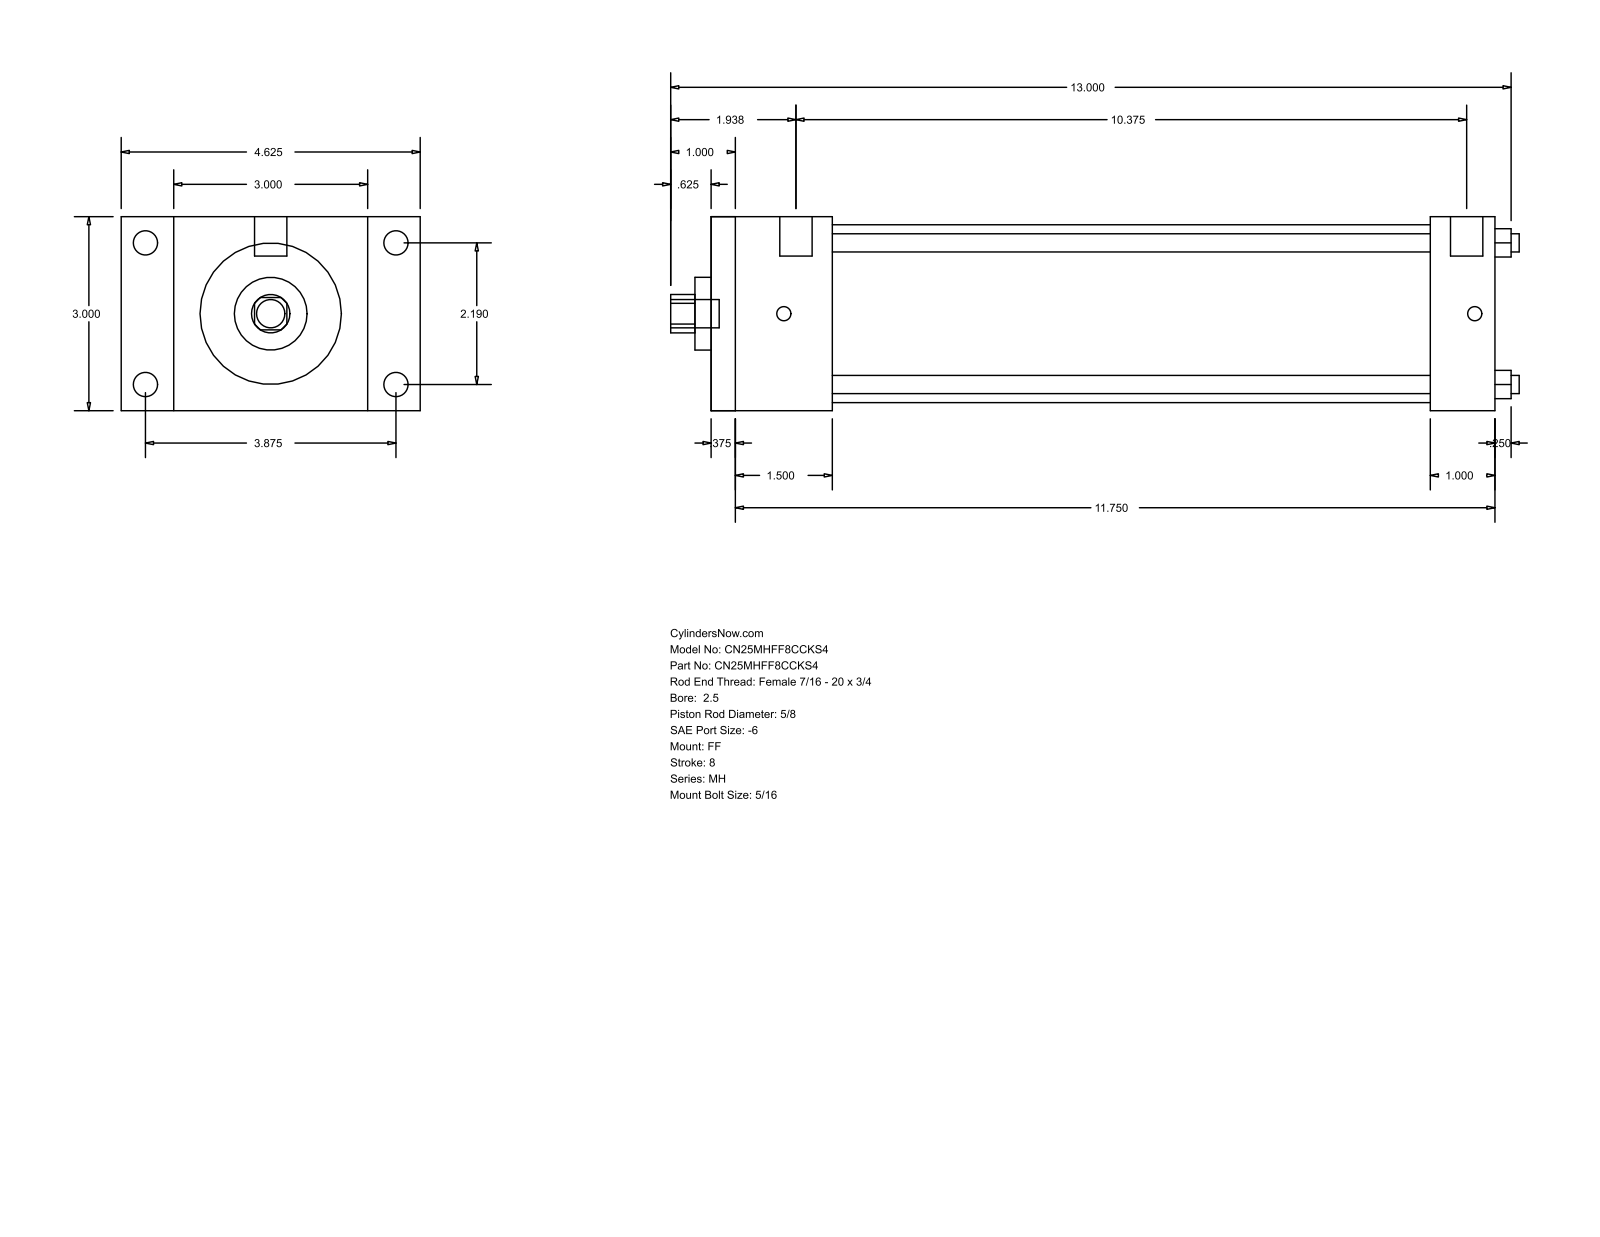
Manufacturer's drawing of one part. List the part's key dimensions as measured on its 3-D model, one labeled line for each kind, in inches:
Part name (STEP PRODUCT): MH_FF__0250_0.625
STEP written by: GSSL Pune (CONFIG_CONTROL_DESIGN)
Units: inches
Bodies: 0 solids, 92 faces (64 planar, 28 cylindrical, 0 other)
Overall size (bounding box): 13.125 × 4.625 × 3
Round holes (diameter × count): ⌀0.281 ×4, ⌀0.625 ×1, ⌀1.125 ×1, ⌀2.75 ×1
Round bosses / shafts (diameter × count): ⌀0.375 ×4, ⌀0.219 ×4, ⌀0.5 ×2, ⌀0.437 ×1
Partial cylindrical surfaces — rounded edges, fillets, slot ends (radius × count): R0.297 ×1
Main face-to-face distances: 3, 12.125, 0.375, 11.75, 1, 1.875, 11.125, 1.5, 10.75, 9.25
Hole centre spacings: 1.548, 2.19, 3.097
